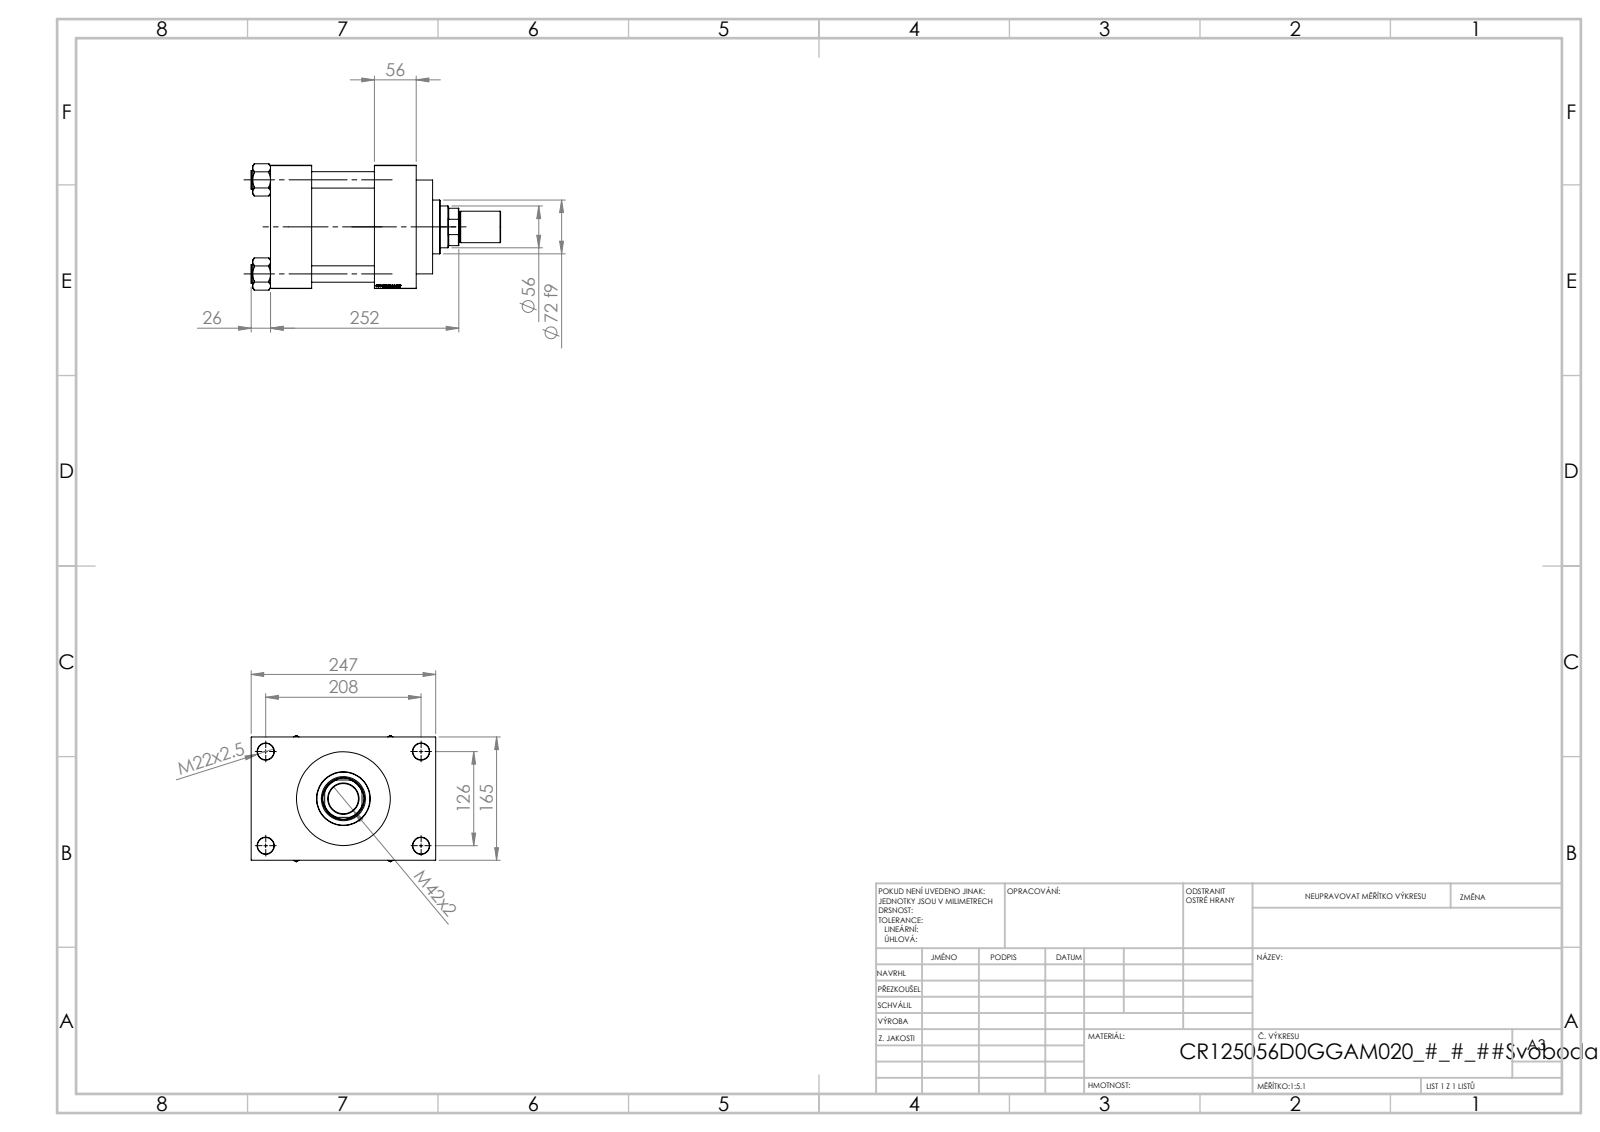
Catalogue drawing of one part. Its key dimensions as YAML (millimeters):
part_name: "NUT_M5_D; ROD_END_AH; V215CR_D_Body; V215CR_VCP_D (+2 more)"
step_written_by: "SolidWorks 2019 (CONFIG_CONTROL_DESIGN)"
units: millimeters
bodies: {solids: 12, faces: 1163, planar: 548, cylindrical: 91, other: 524}
overall_size: [334, 247, 169.14]
volume: 5035000
surface_area: 540193
round_holes:
  - {diameter: 22, count: 8}
  - {diameter: 7, count: 2}
  - {diameter: 32.24, count: 2}
  - {diameter: 45, count: 2}
  - {diameter: 40.5, count: 1}
  - {diameter: 56, count: 1}
  - {diameter: 59, count: 1}
  - {diameter: 96, count: 1}
  - {diameter: 125, count: 1}
  - {diameter: 125.5, count: 1}
round_bosses_or_shafts:
  - {diameter: 25, count: 4}
  - {diameter: 131, count: 1}
  - {diameter: 72, count: 1}
  - {diameter: 42, count: 1}
  - {diameter: 40, count: 1}
partial_cylinders:
  - {radius: 27, count: 1}
face_to_face_distances: [165, 84, 55, 139, 56, 195, 140, 41, 206, 173.74]
hole_center_spacings: [41.05, 89.02, 121.59, 125.9, 132.47, 166.95, 209.13, 126]
